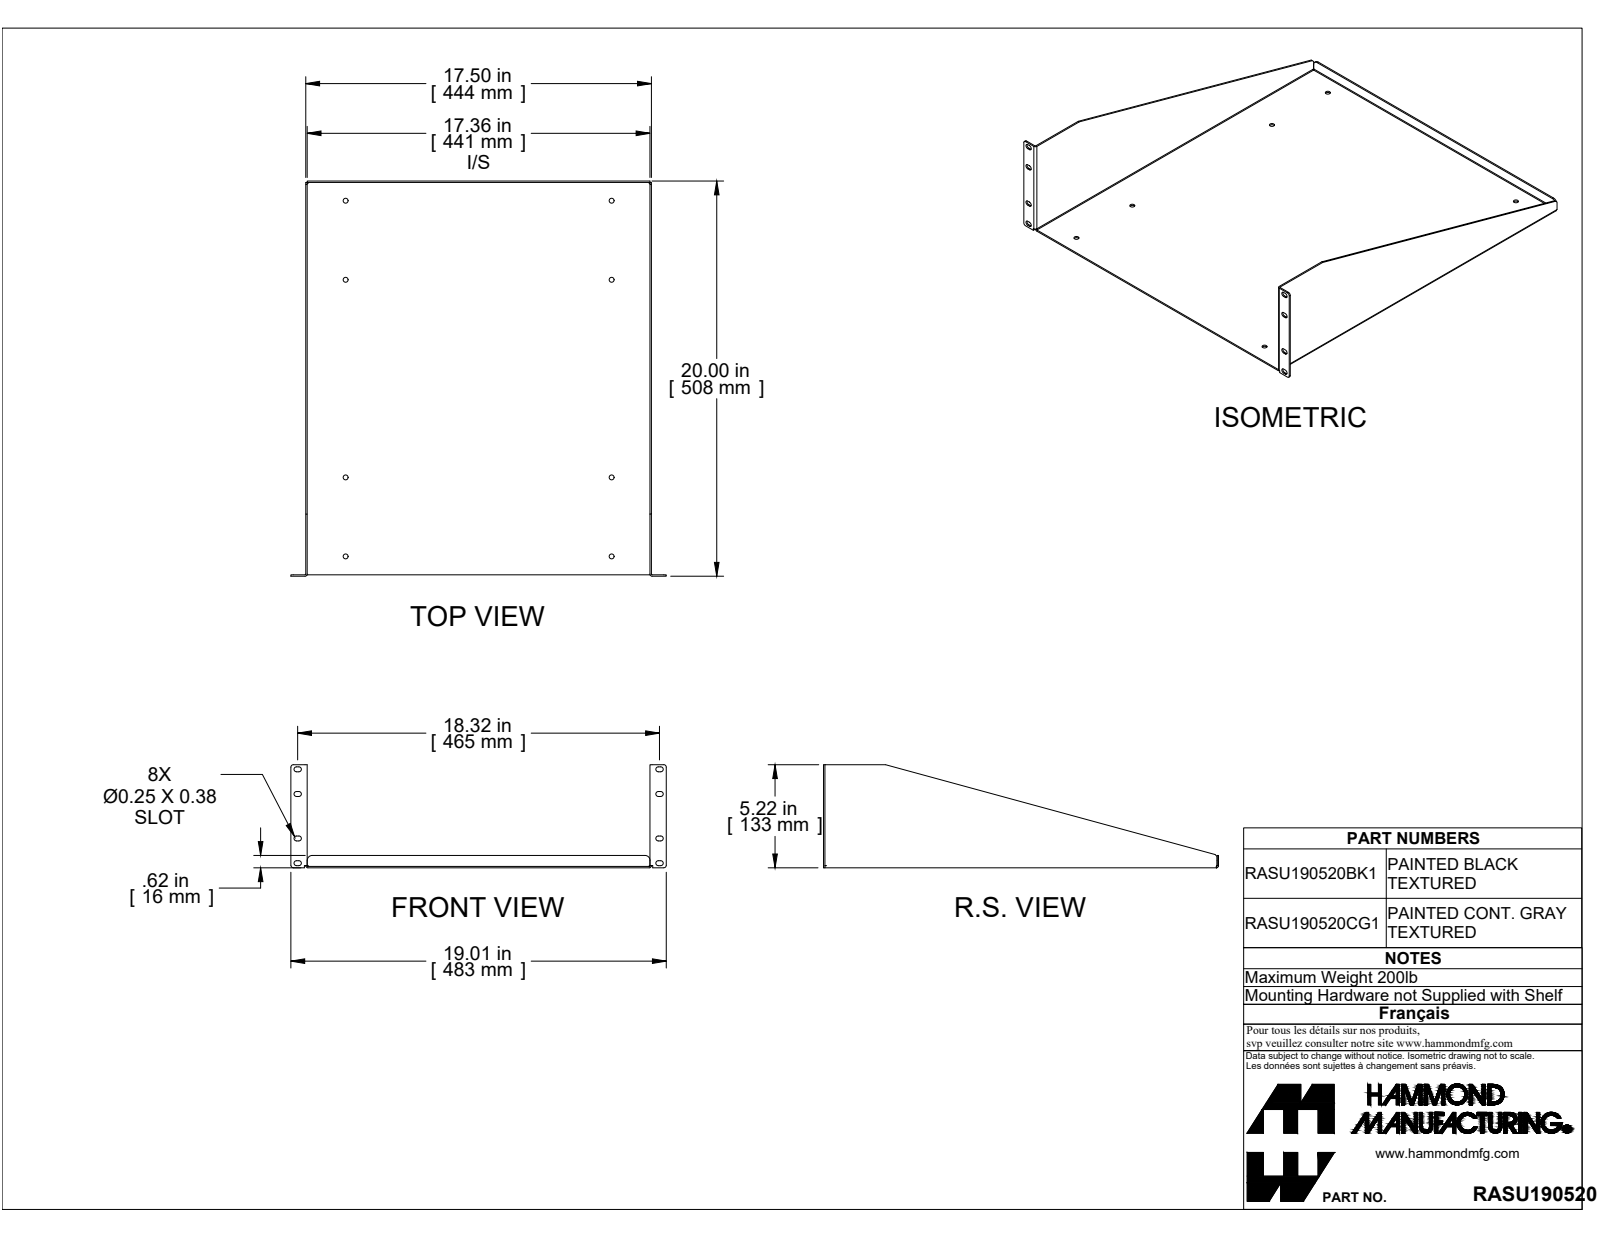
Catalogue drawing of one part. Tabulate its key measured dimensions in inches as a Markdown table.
| quantity | value |
| --- | --- |
| part name | RASU190520BK1 |
| STEP written by | SolidWorks 2019 (CONFIG_CONTROL_DESIGN) |
| units | inches |
| bodies | 1 solid, 104 faces (56 planar, 44 cylindrical, 4 other) |
| overall size | 20 × 19.006 × 5.218 |
| volume | 35.38 in³ |
| surface area | 990.4 in² |
| round holes (diameter × count) | 0.25 × 8 |
| partial cylindrical surfaces (radius × count) | 0.125 × 20, 0.036 × 5, 0.108 × 5, 0.055 × 3, 0.25 × 2 |
| main face-to-face distances | 0.072, 17.428, 17.356, 17.5, 19.856, 19.928, 0.072, 19.928, 20, 0.625 |
| hole center spacings | 4, 13.468, 14, 14.049, 19.426, 10, 16.774, 18 |
